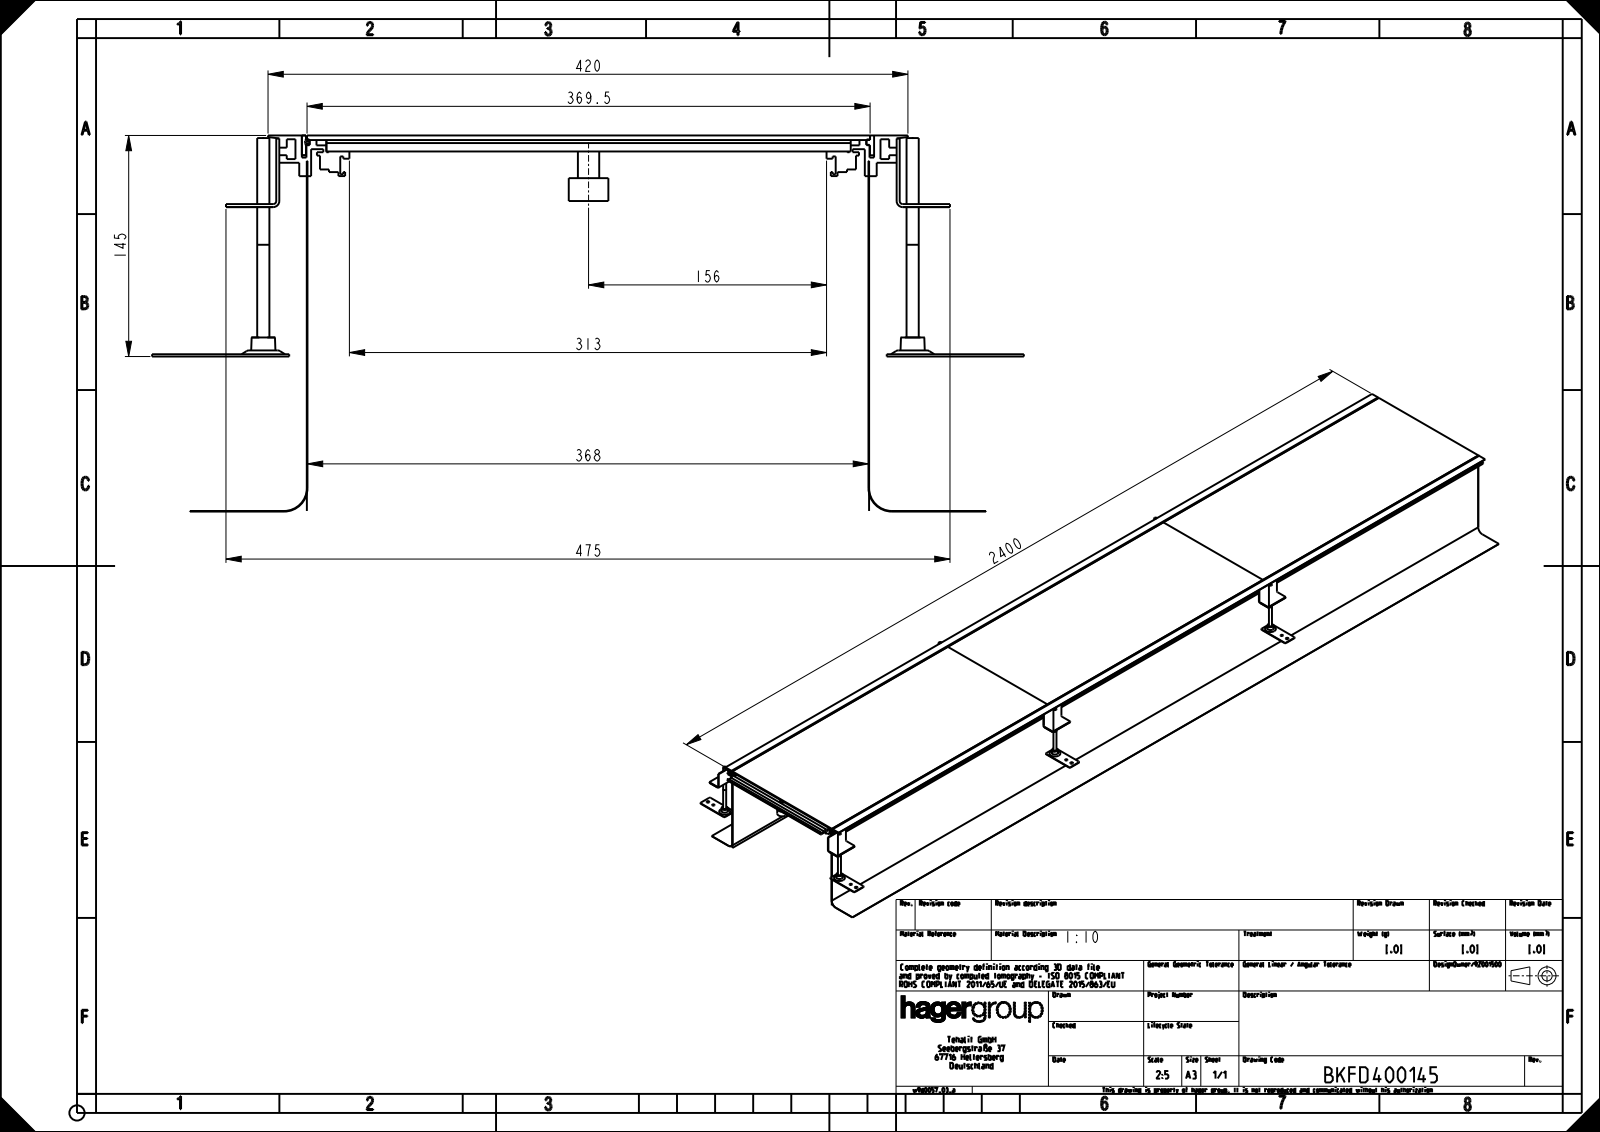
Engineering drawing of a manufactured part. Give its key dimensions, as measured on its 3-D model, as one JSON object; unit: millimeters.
{"part_name": "U05644KUN; U05650KUN; U05994KUN; U05647KUN (+8 more)", "step_written_by": "CREO PARAMETRIC BY PTC INC, 2020281 (AUTOMOTIVE_DESIGN)", "units": "millimeters", "bodies": {"solids": 62, "faces": 1026, "planar": 600, "cylindrical": 354, "other": 72}, "overall_size": [2432.5, 572.13, 246.7], "volume_mm3": 7285000, "surface_area_mm2": 6928000, "round_holes": [[7, 15], [8, 9], [10, 9], [6, 6], [8.5, 6], [11.5, 6], [17.5, 6], [23, 6]], "round_bosses_or_shafts": [[26, 9], [14, 9], [11.9, 9], [20, 6], [8, 6]], "partial_cylinders_radius": [[2, 92], [3, 24], [0.5, 20], [4, 2], [15, 2], [15.4, 2]], "face_to_face_distances": [0.4, 368.55, 3, 368.95, 368.15, 243.7, 246.7, 243.3, 246.3, 6.5], "hole_center_spacings": [800, 1600, 800.25, 801.1, 802.4, 926.9, 937.16, 959.71]}
